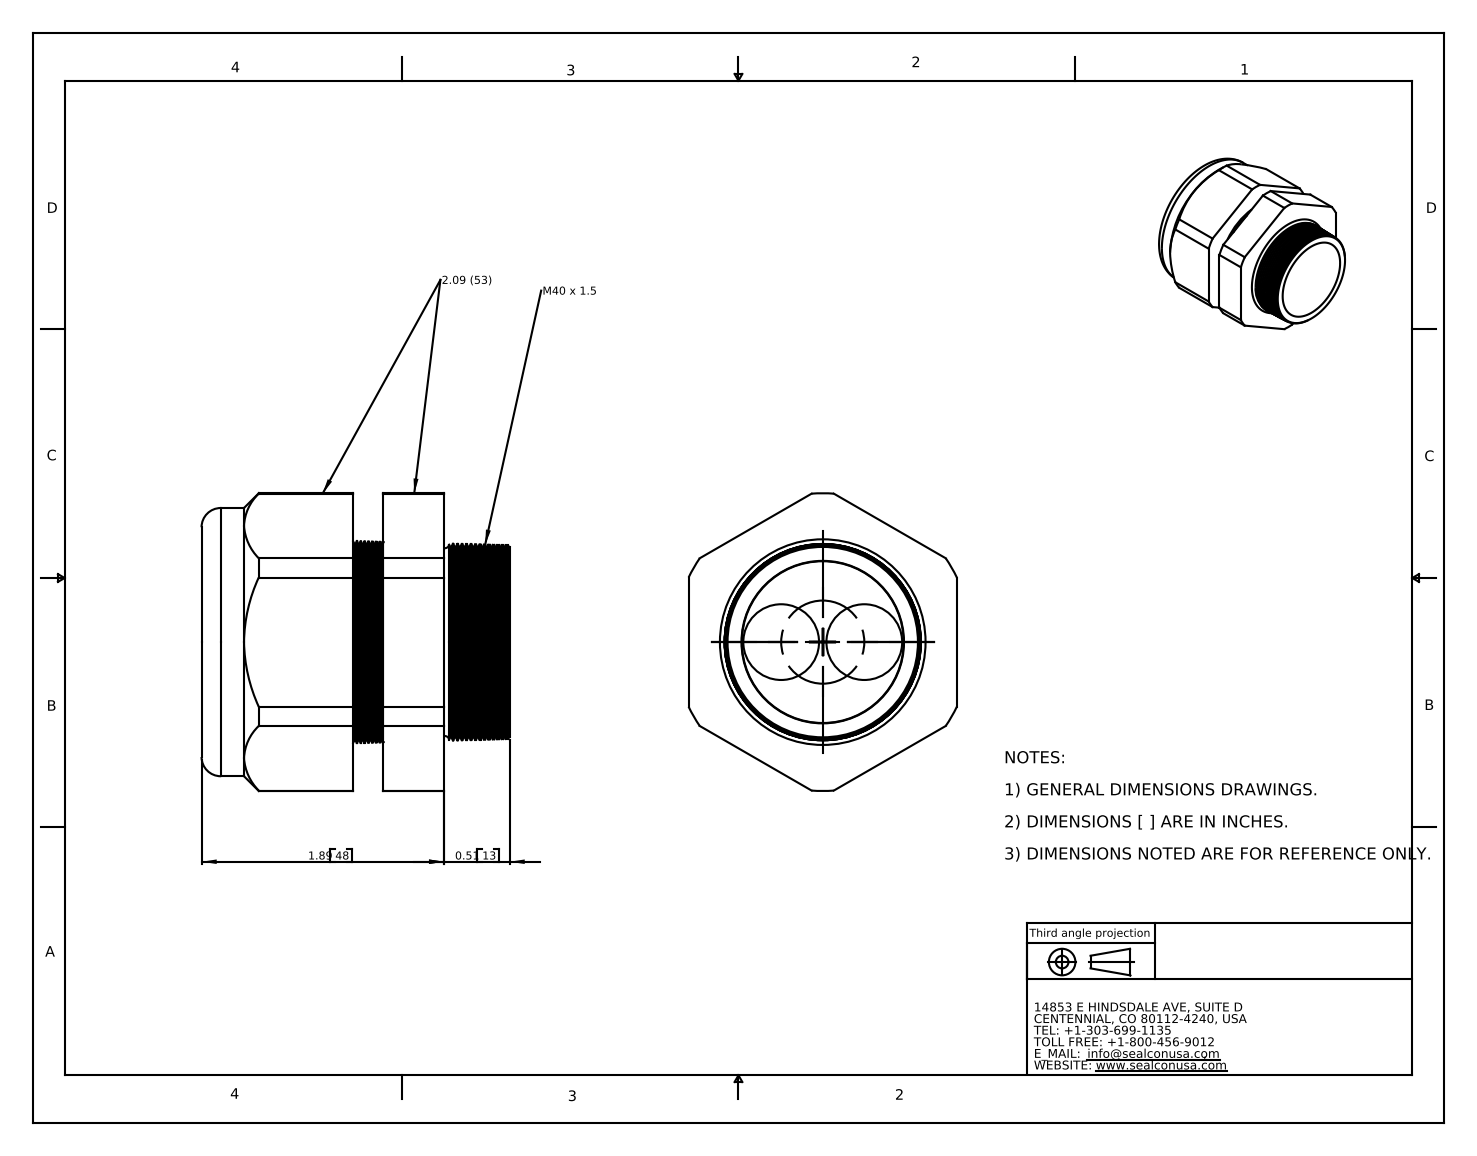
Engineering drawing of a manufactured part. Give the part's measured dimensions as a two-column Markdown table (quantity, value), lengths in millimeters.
| quantity | value |
| --- | --- |
| part name | CD40M4-GY |
| STEP written by | SolidWorks 2007 (CONFIG_CONTROL_DESIGN) |
| units | millimeters |
| bodies | 2 solids, 193 faces (21 planar, 24 cylindrical, 148 other) |
| overall size | 61 × 58.9 × 53.1 |
| volume | 77 580 mm³ |
| surface area | 26 350 mm² |
| round holes (diameter × count) | 15 × 2, 31.5 × 1, 32 × 1 |
| round bosses / shafts (diameter × count) | 53.1 × 1 |
| partial cylindrical surfaces (radius × count) | 29.5 × 1 |
| main face-to-face distances | 53.1, 6, 18, 12, 30, 36, 48, 12.7, 17.3, 23.3 |
| hole center spacings | 8.2, 16.5 |
